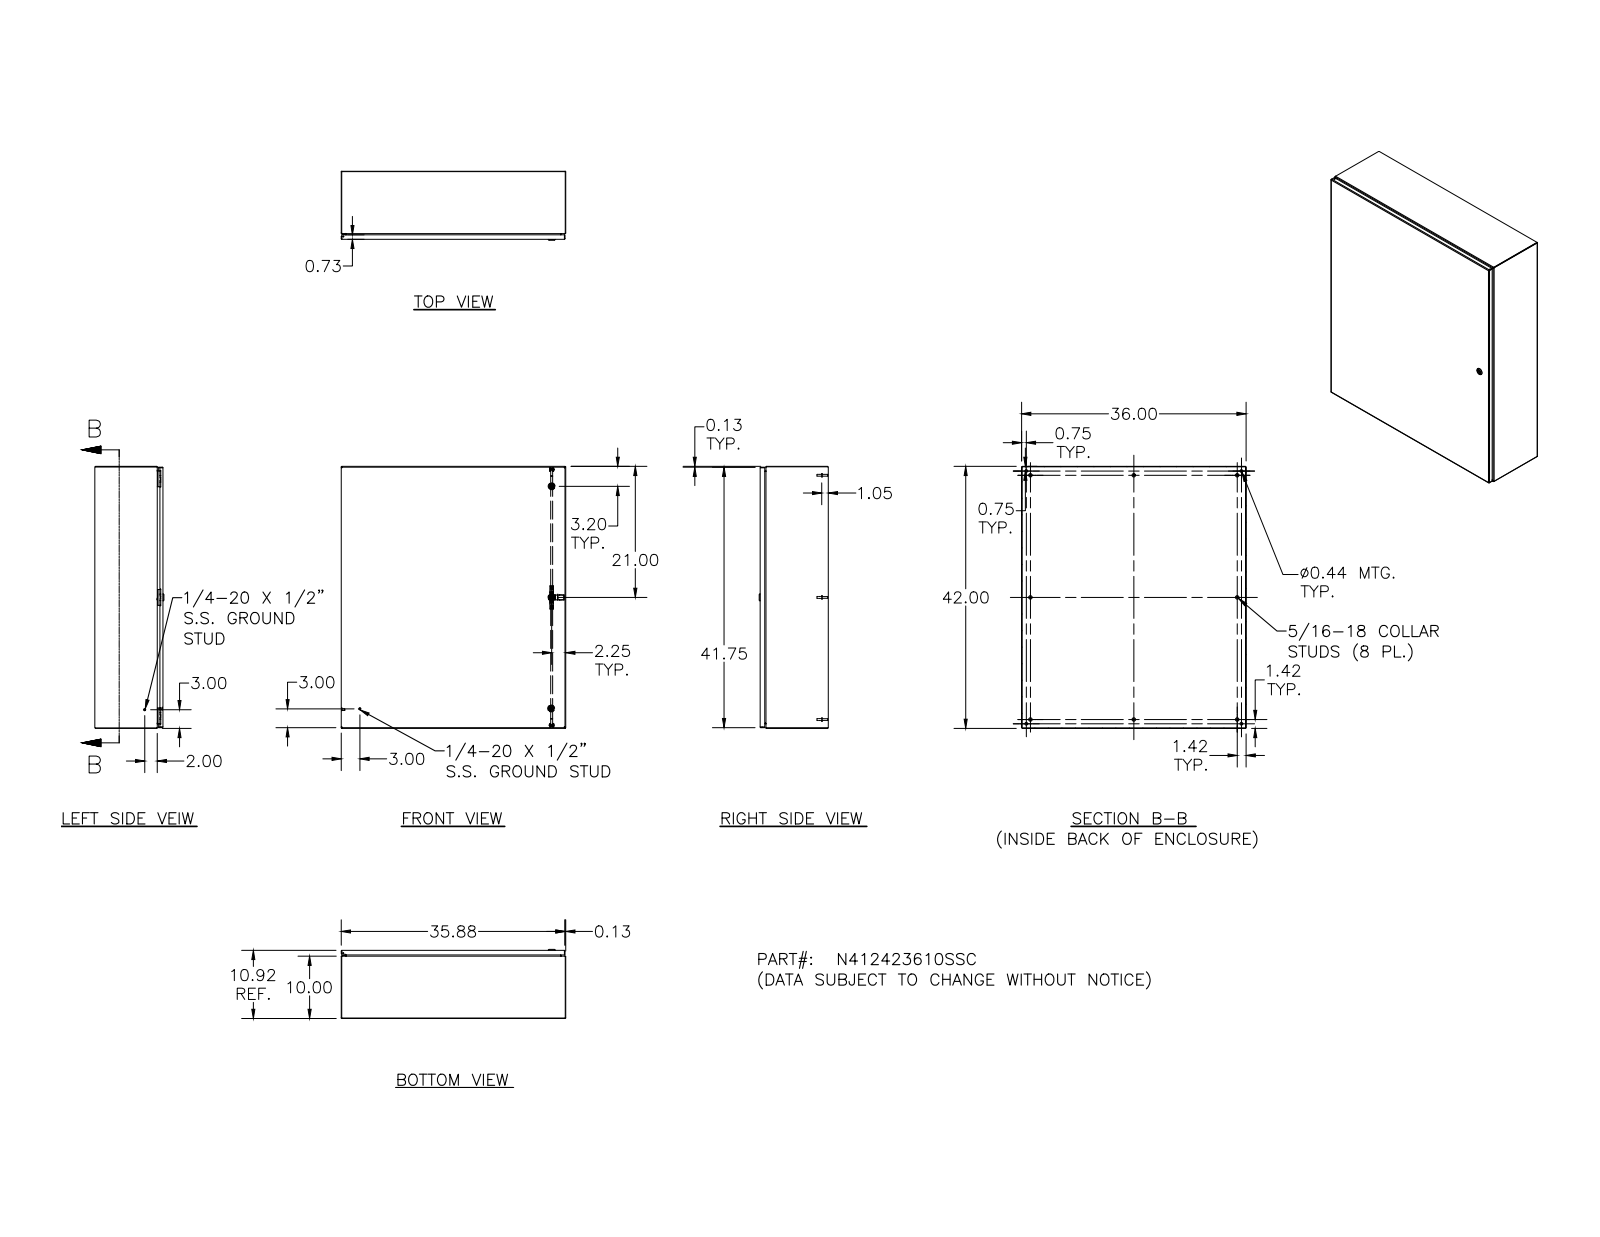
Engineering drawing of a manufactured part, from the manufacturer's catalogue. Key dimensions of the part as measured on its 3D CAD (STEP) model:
Part name (STEP PRODUCT): N412423610SSC; N412423610SSCBLR; N4123610SSCTB; 388151 (+8 more)
STEP written by: Autodesk Inventor 2011 (AUTOMOTIVE_DESIGN)
Units: inches
Bodies: 72 solids, 2241 faces (871 planar, 820 cylindrical, 550 other)
Overall size (bounding box): 42 × 36 × 11.075
Volume: 366.9 in³ · Surface area: 9 896 in²
Round holes (diameter × count): ⌀0.093 ×6, ⌀0.152 ×6, ⌀0.167 ×6, ⌀0.172 ×6, ⌀0.187 ×6, ⌀0.197 ×5, ⌀0.165 ×4, ⌀0.438 ×4, ⌀0.156 ×3, ⌀0.106 ×2, ⌀0.16 ×2, ⌀0.169 ×2
Round bosses / shafts (diameter × count): ⌀0.25 ×14, ⌀0.563 ×8, ⌀0.3 ×8, ⌀0.275 ×8, ⌀0.36 ×6, ⌀0.32 ×6, ⌀0.256 ×6, ⌀0.164 ×6
Partial cylindrical surfaces — rounded edges, fillets, slot ends (radius × count): R0.05 ×38, R0.031 ×32, R0.012 ×31, R0.016 ×26, R0.125 ×24, R0.02 ×20, R0.105 ×18, R0.118 ×18
Main face-to-face distances: 0.074, 10.843, 10.769, 10.917, 35.926, 41.926, 35.852, 36, 41.852, 42
Hole centre spacings: 19, 38, 19.007, 0.5, 0.656, 0.66, 1.307, 1.311
